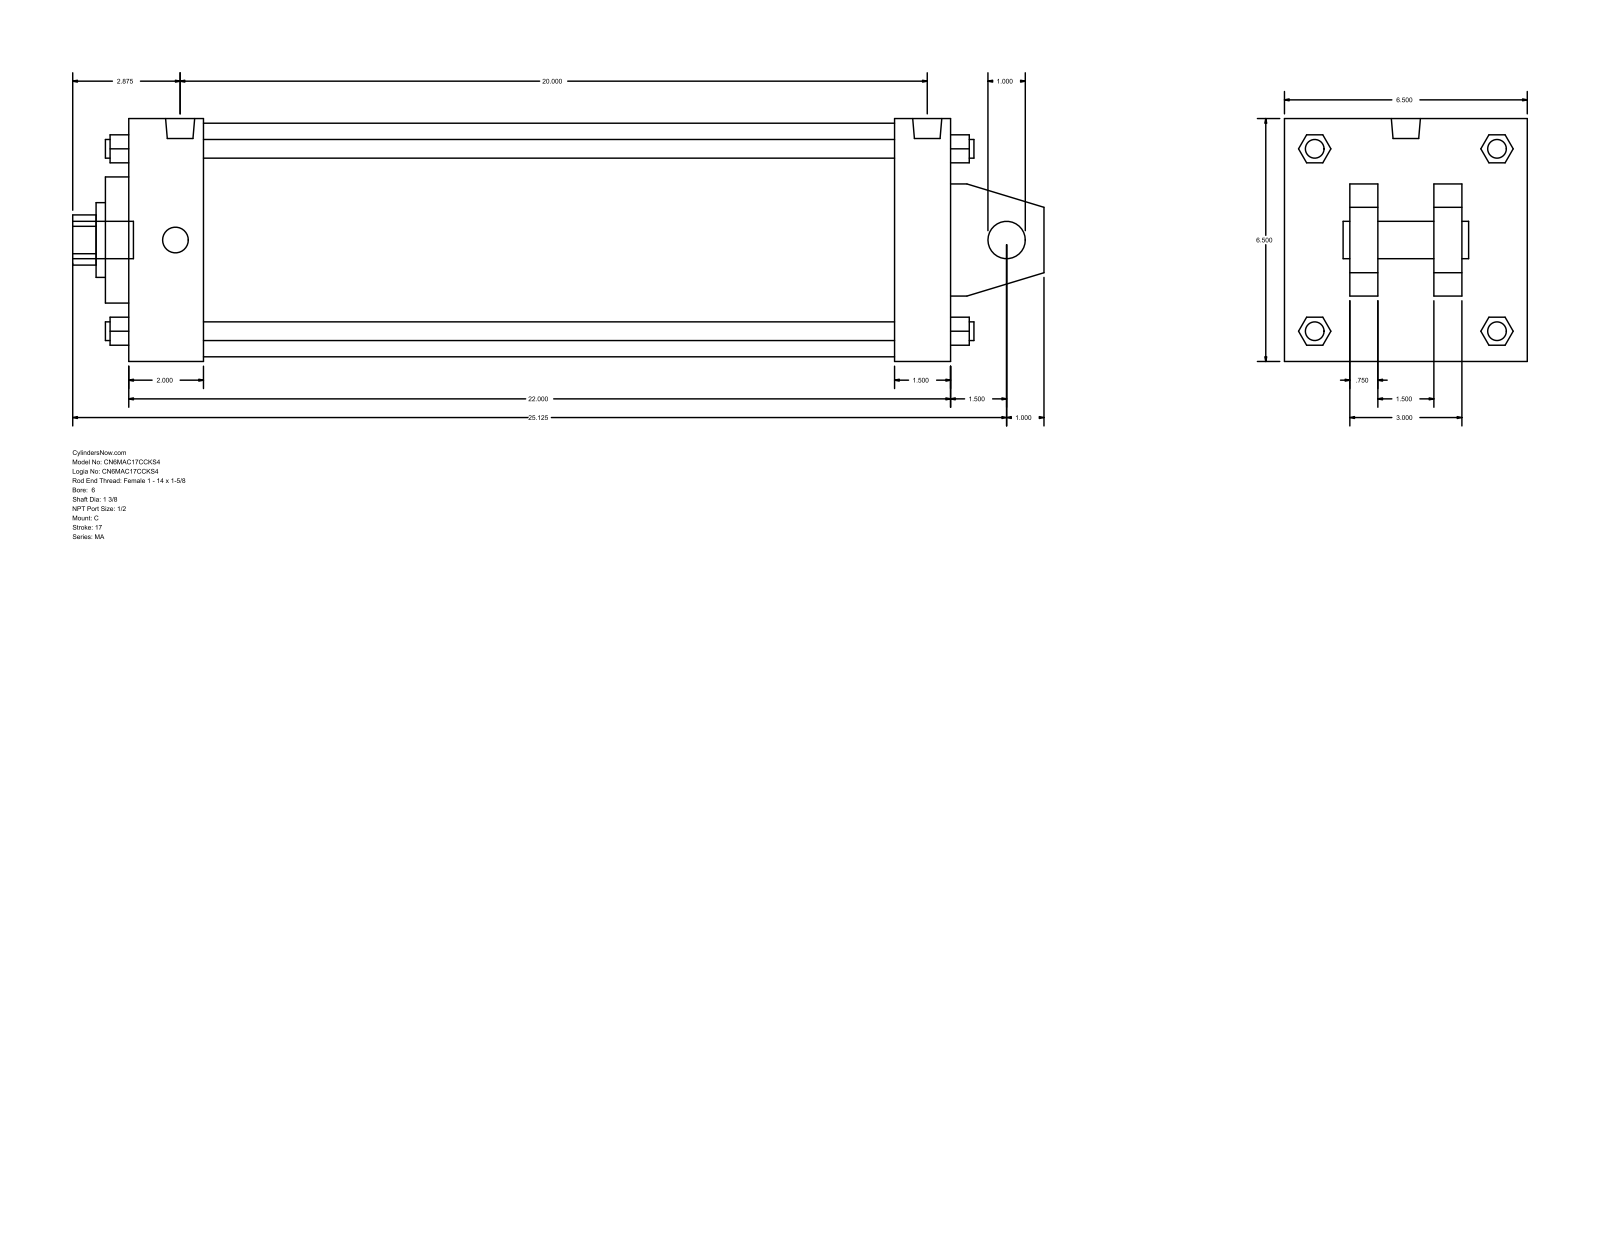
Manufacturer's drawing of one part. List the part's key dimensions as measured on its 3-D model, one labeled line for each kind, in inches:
Part name (STEP PRODUCT): MA_C__0600_1.375
STEP written by: GSSL Pune (CONFIG_CONTROL_DESIGN)
Units: inches
Bodies: 0 solids, 141 faces (109 planar, 32 cylindrical, 0 other)
Overall size (bounding box): 26 × 6.5 × 6.5
Round holes (diameter × count): ⌀1 ×1, ⌀1.375 ×1, ⌀2 ×1, ⌀3.375 ×1, ⌀6.25 ×1
Round bosses / shafts (diameter × count): ⌀0.687 ×4, ⌀0.5 ×4, ⌀0.778 ×2, ⌀1 ×1
Partial cylindrical surfaces — rounded edges, fillets, slot ends (radius × count): R0.672 ×1
Main face-to-face distances: 6.5, 22, 1.5, 0.75, 2.5, 4, 2, 1.75, 4.75, 20.5
